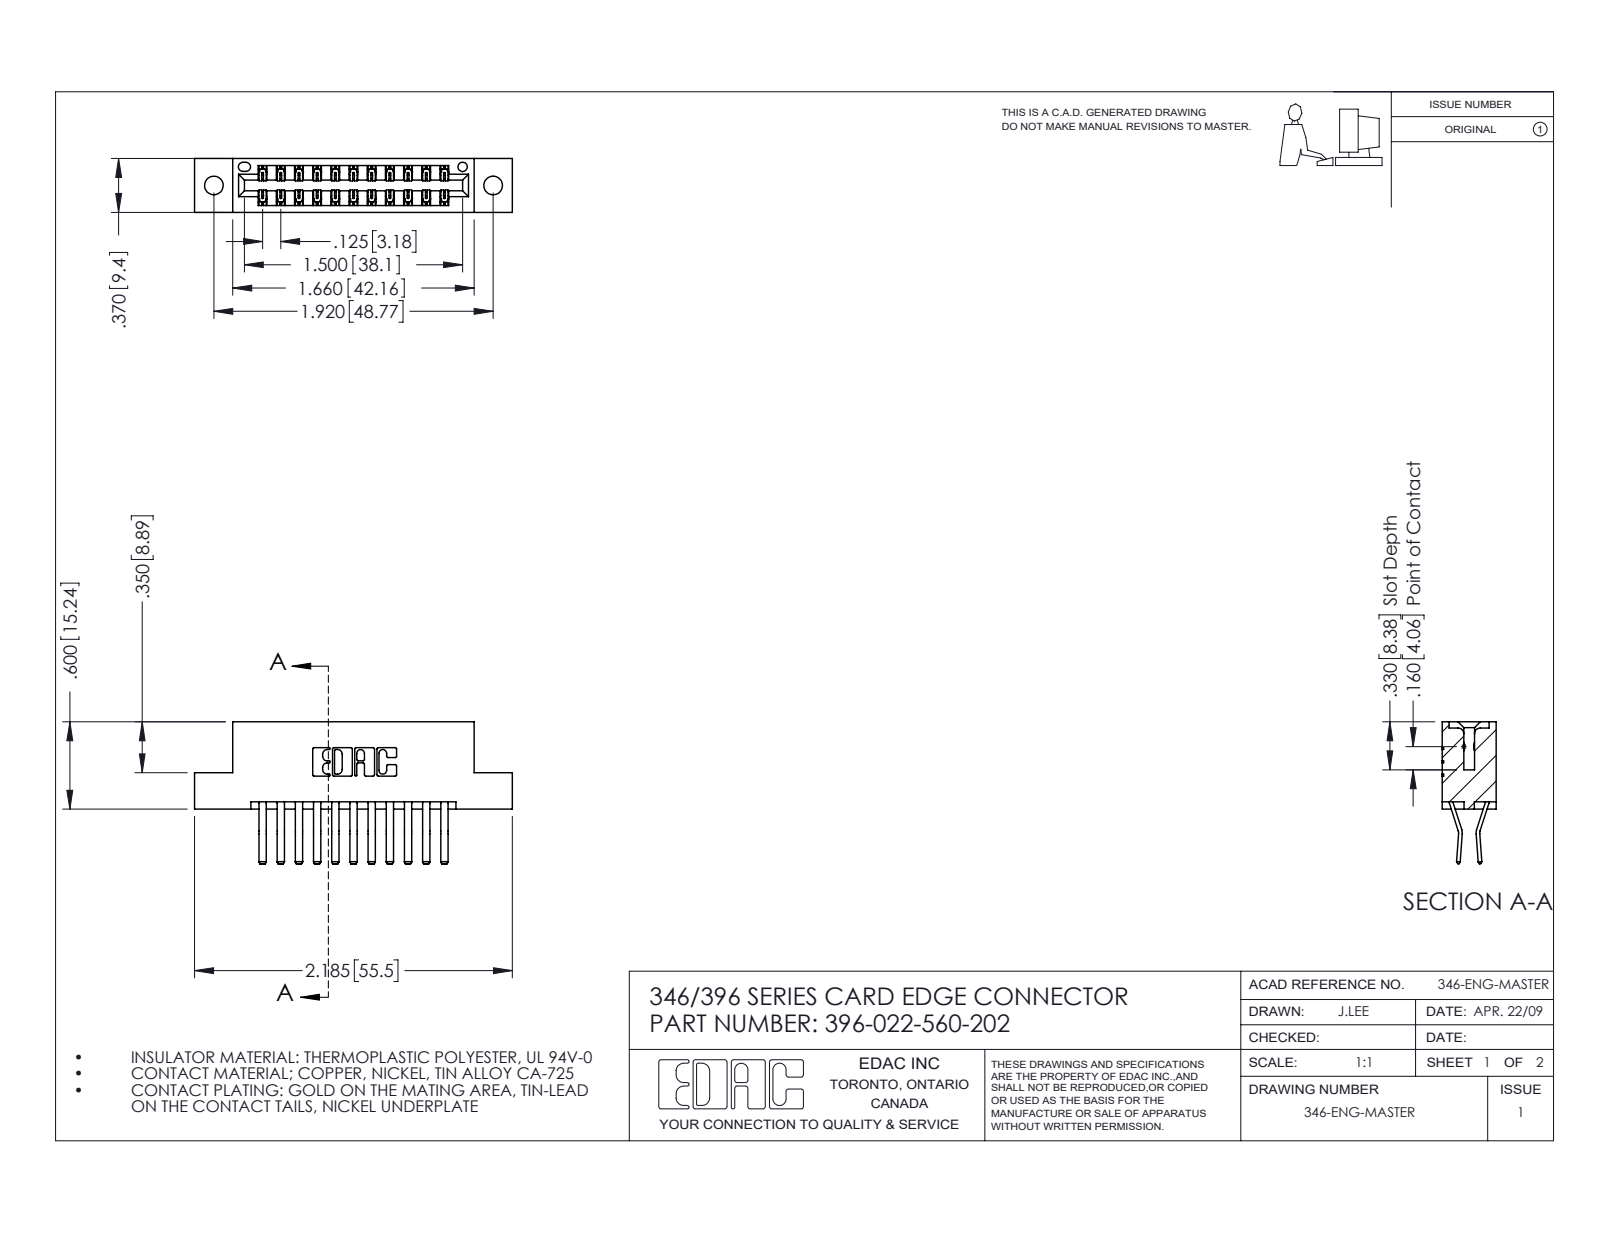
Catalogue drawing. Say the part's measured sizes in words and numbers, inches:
The part is named "346 Part_Flush Mounting Lugs - 0.128 Dia; 396-022-560-202; 345-292-001_560 Tail". Its 3-D file was written by "SolidWorks 2016 (CONFIG_CONTROL_DESIGN)". It is 23 solids with 1310 faces: 846 planar, 464 cylindrical and 0 other. Overall it measures 2.185 by 0.975 by 0.37 inches. Its volume is 0.322 cubic inches and its surface area 10.67 square inches. Round holes: 2 of diameter 0.128, 1 of diameter 0.064. Partial cylindrical surfaces (rounded edges, fillets, slot ends): 33 of radius 0.006, 22 of radius 0.01, 6 of radius 0.007, 6 of radius 0.031, 3 of radius 0.026, 2 of radius 0.01, 2 of radius 0.014, 2 of radius 0.022. The main face-to-face distances are 0.25, 0.048, 0.322, 0.37, 0.025, 0.072, 0.298, 0.275, 0.148, 0.222. The hole center spacings are 0.246, 1.715, 1.92.
